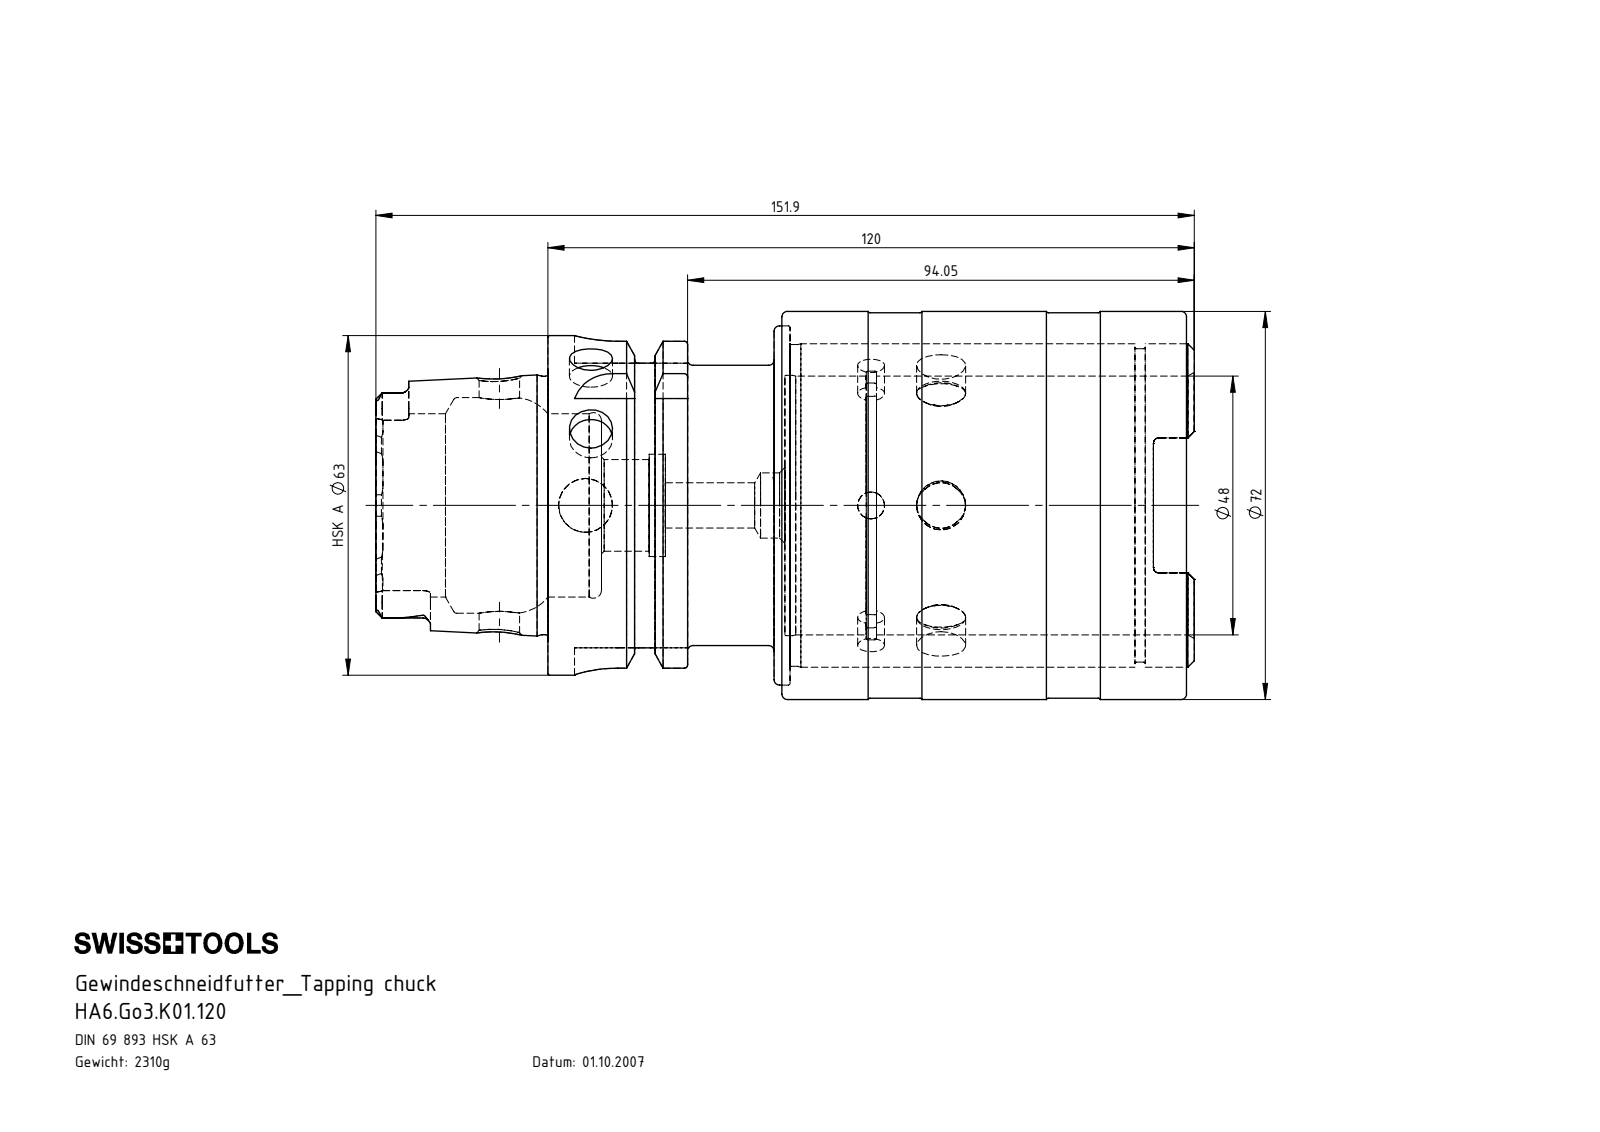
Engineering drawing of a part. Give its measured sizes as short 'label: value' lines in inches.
name: HA6.Go3.K01.120; Einbausatz Go3_gespannt; Kugel Go3; Hülse Go3 (+6 more)
written by: SolidWorks 2011 (AUTOMOTIVE_DESIGN)
unit: in
bodies: 10 solids, 398 faces (91 planar, 124 cylindrical, 183 other)
size: 5.98 × 2.835 × 2.835
volume: 17.94 in³; area: 164.4 in²
holes: 3× ⌀0.197, 3× ⌀0.358, 2× ⌀0.315, 1× ⌀0.118, 1× ⌀0.295, 1× ⌀0.331, 1× ⌀0.394, 1× ⌀0.472, 1× ⌀0.476, 1× ⌀0.669, 1× ⌀0.748, 1× ⌀1.339
bosses: 1× ⌀2.835, 1× ⌀2.815, 1× ⌀2.624, 1× ⌀2.48, 1× ⌀2.362, 1× ⌀2.35, 1× ⌀2.289, 1× ⌀2.163
rounds: 6× R0.055, 4× R0.113, 4× R0.315, 3× R0.167, 2× R0.039
face distances: 0.748, 0.73, 0.768, 0.02, 0.098, 2.656, 1.77, 0.037, 0.018, 0.923
hole spacings: 0.512, 2.047, 2.087, 2.559, 2.598
